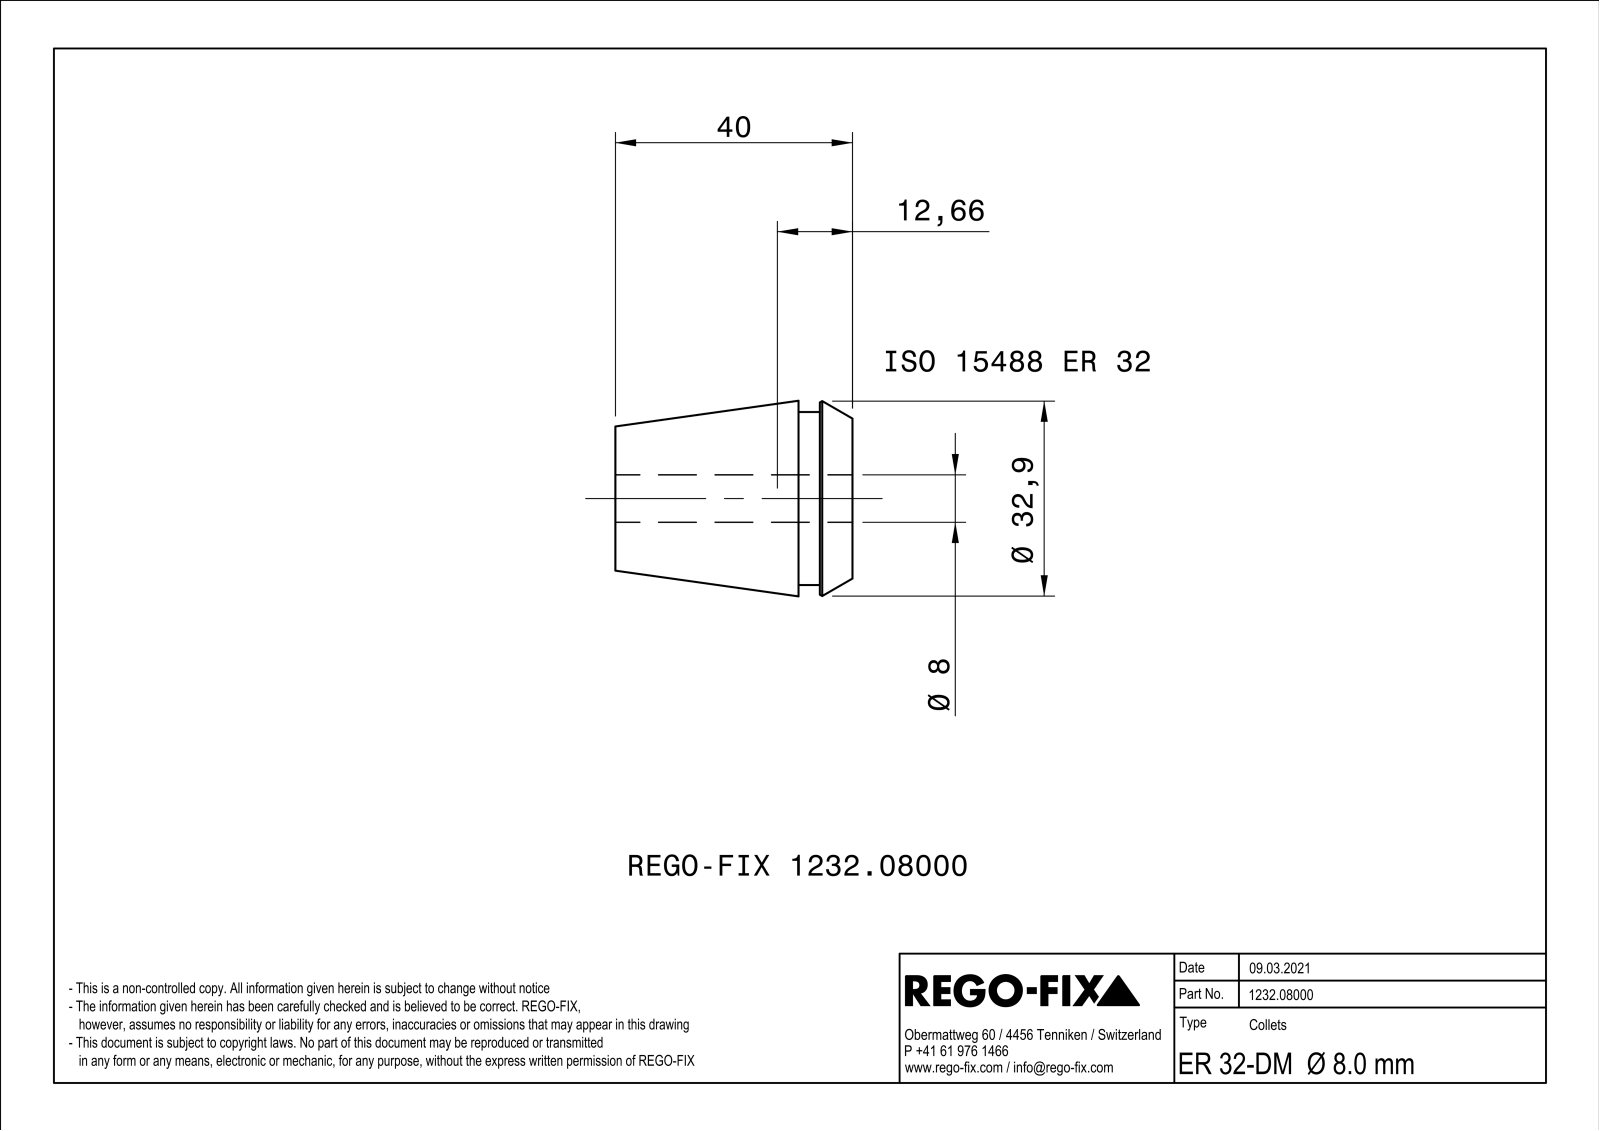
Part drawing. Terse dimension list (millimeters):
name: NOCUT
written by: SIEMENS PLM Software Solid Edge ST10 (AUTOMOTIVE_DESIGN)
unit: mm
bodies: 1 solid, 154 faces (80 planar, 9 cylindrical, 65 other)
size: 40 × 32.99 × 32.99
volume: 20 502 mm³; area: 15 033 mm²
holes: 1× ⌀8
bosses: 1× ⌀29.2
face distances: 0.8, 40, 9.1, 30.9, 5.5, 3.6, 34.5, 16, 10.5, 6.9
